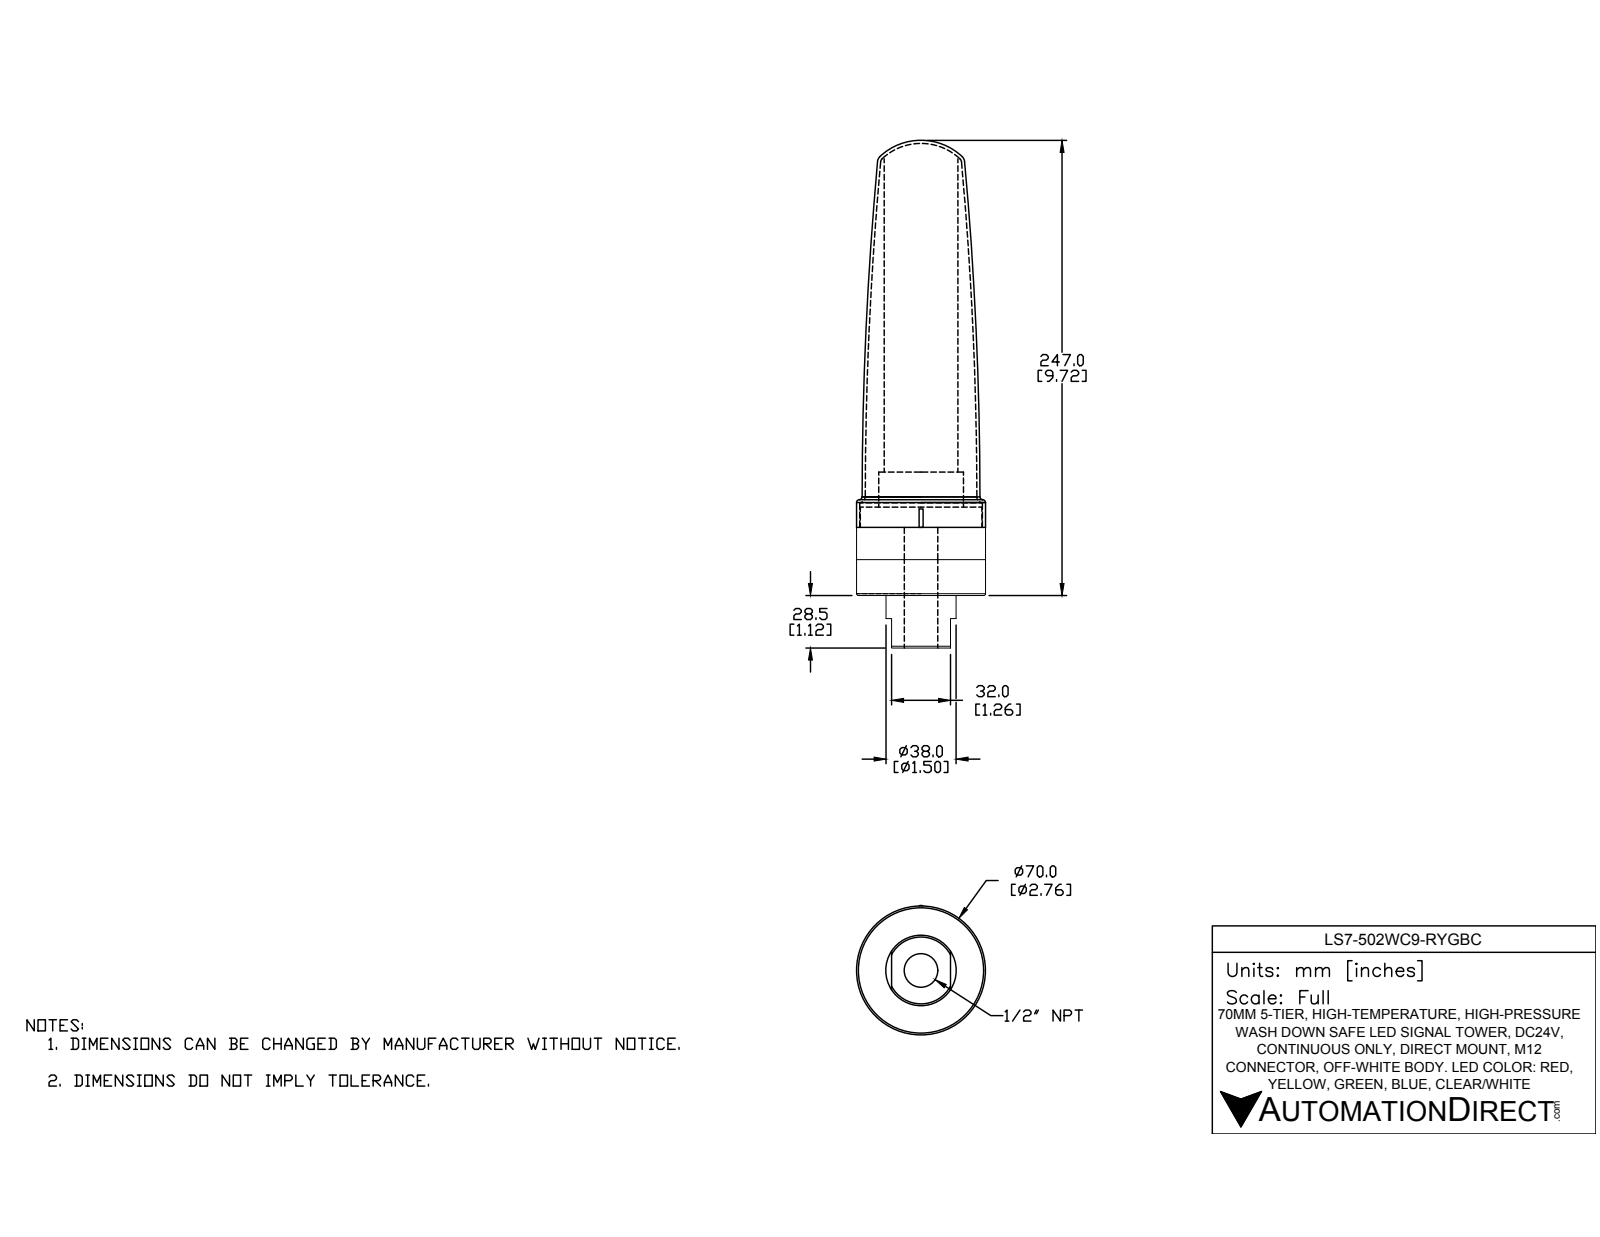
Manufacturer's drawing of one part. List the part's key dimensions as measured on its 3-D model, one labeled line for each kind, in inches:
Part name (STEP PRODUCT): LS7-502WC9-RYGBC
STEP written by: SolidWorks 2016 (AUTOMOTIVE_DESIGN)
Units: inches
Bodies: 4 solids, 60 faces (17 planar, 20 cylindrical, 23 other)
Overall size (bounding box): 10.846 × 2.768 × 2.756
Volume: 28.8 in³ · Surface area: 207.4 in²
Round holes (diameter × count): ⌀0.717 ×1, ⌀2.622 ×1
Round bosses / shafts (diameter × count): ⌀2.756 ×1, ⌀1.811 ×1, ⌀1.575 ×1, ⌀1.496 ×1
Partial cylindrical surfaces — rounded edges, fillets, slot ends (radius × count): R0.039 ×1, R0.079 ×1
Main face-to-face distances: 1.398, 0.768, 2.165, 1.457, 0.689, 0.709, 9.04, 8.272, 7.583, 6.875
